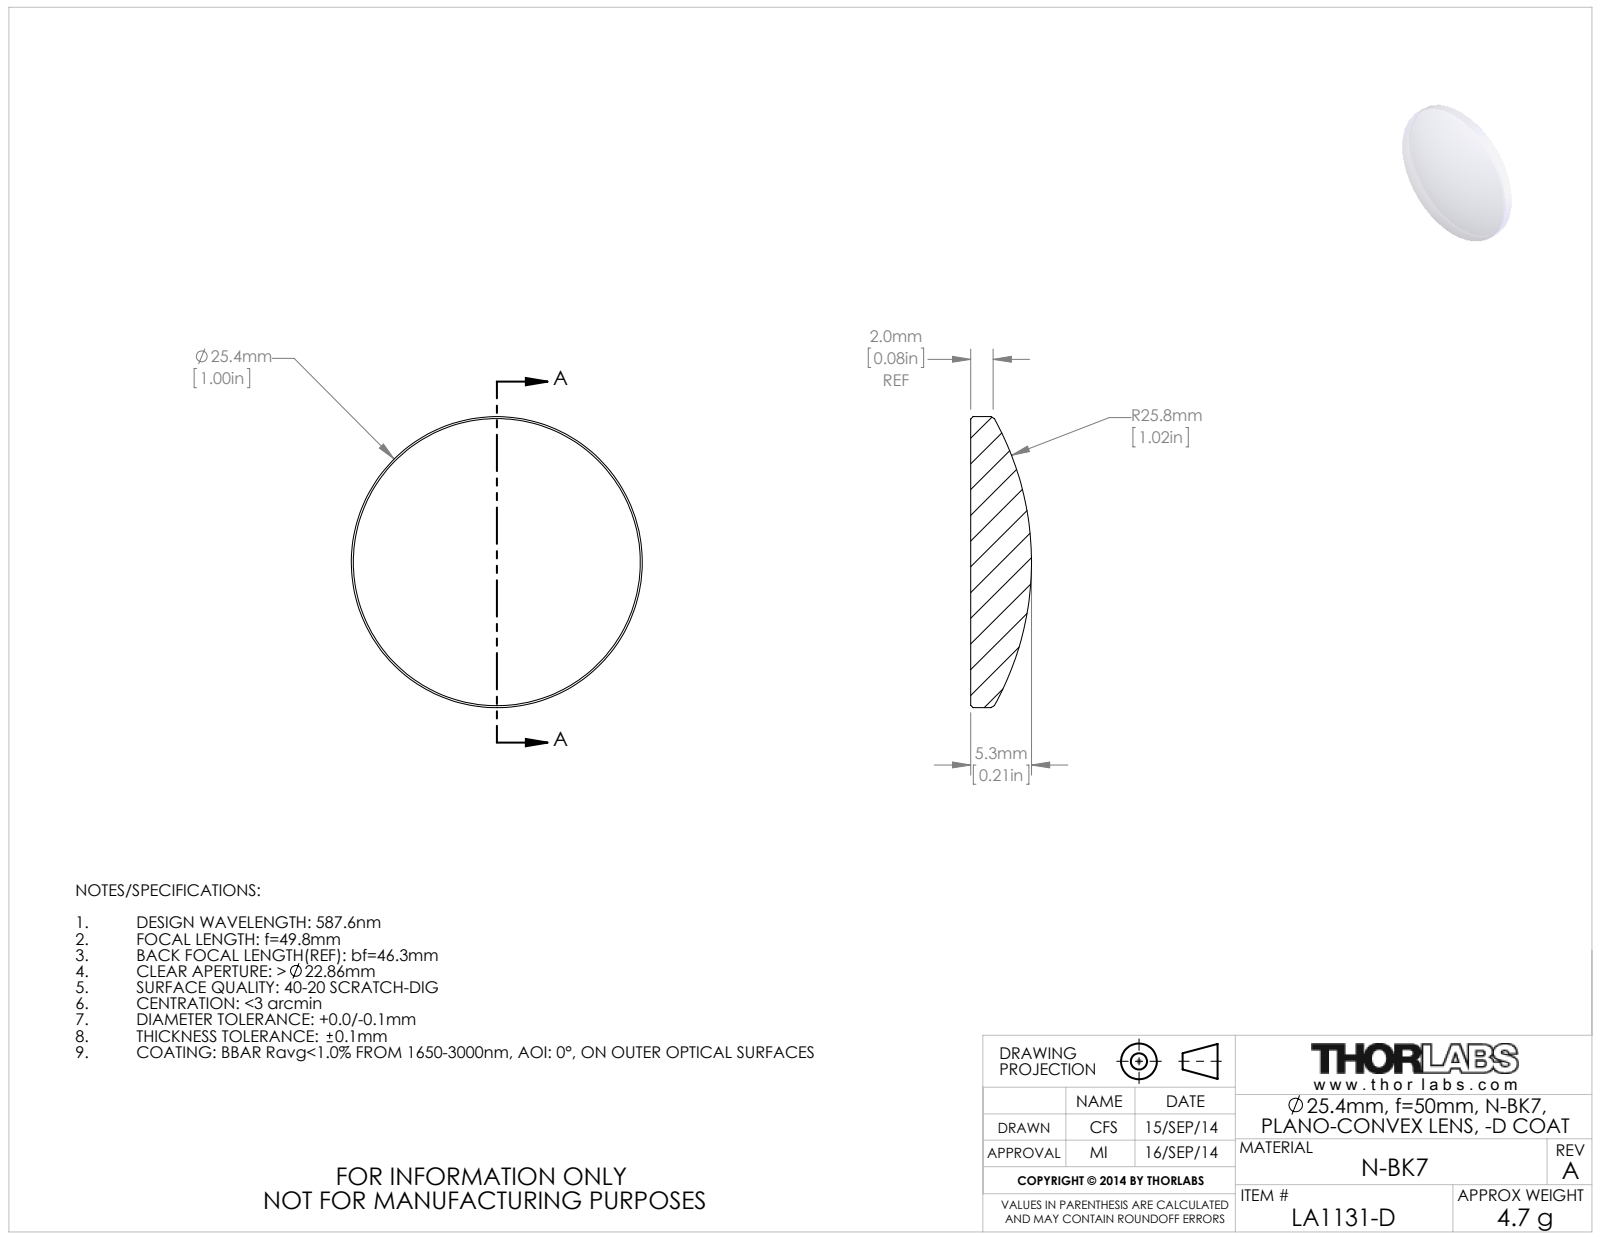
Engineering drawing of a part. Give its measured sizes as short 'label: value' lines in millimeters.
name: TTN031783-E0W
written by: SolidWorks 2014 (CONFIG_CONTROL_DESIGN)
unit: mm
bodies: 1 solid, 9 faces (1 planar, 2 cylindrical, 6 other)
size: 25.4 × 25.4 × 5.3
volume: 1 850 mm³; area: 1 191 mm²
bosses: 1× ⌀25.4
